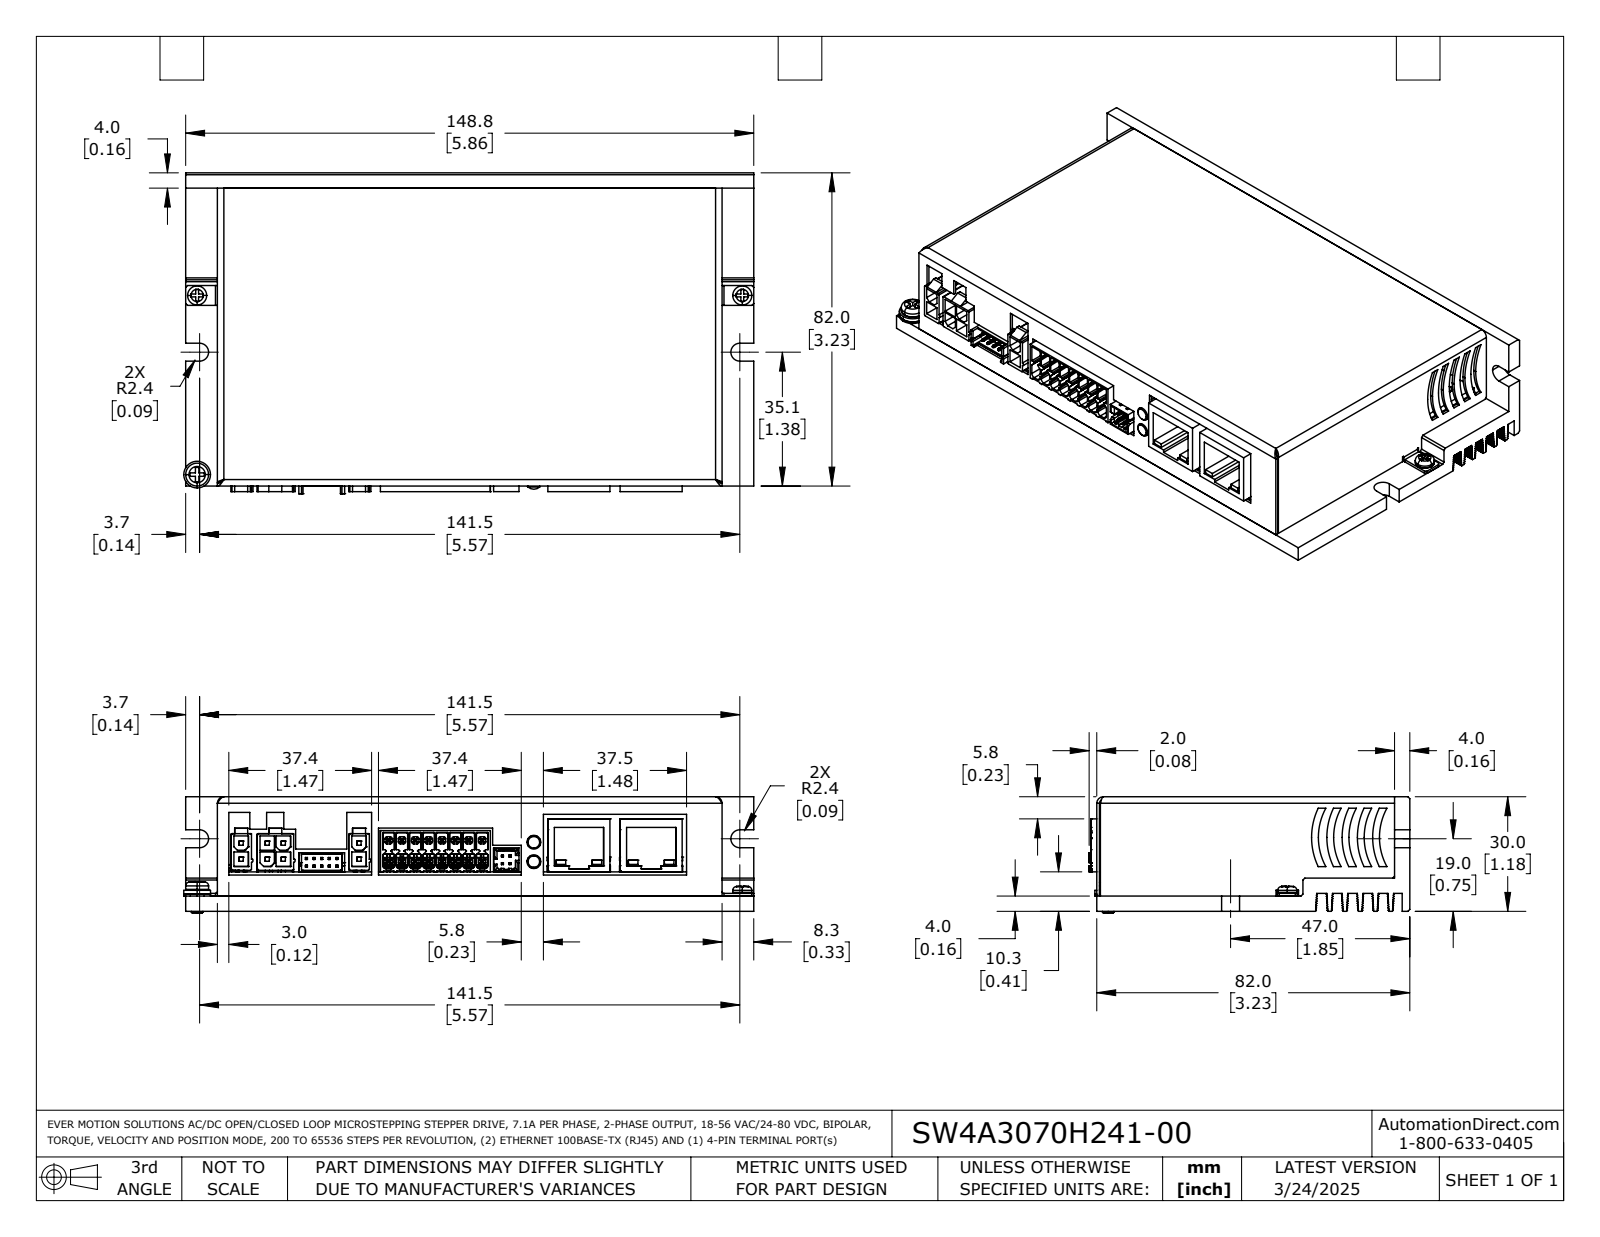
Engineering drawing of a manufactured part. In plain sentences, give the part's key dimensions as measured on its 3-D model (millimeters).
The part is named "SW4A3070H241-00C0680". Its 3-D file was written by "SolidWorks 2024 (AUTOMOTIVE_DESIGN)". It is 21 solids with 3854 faces: 2524 planar, 1109 cylindrical and 221 other. Overall it measures 149.3 by 84 by 30.5 millimeters. Its volume is 105 900 cubic millimeters and its surface area 111 800 square millimeters. Round holes: 30 of diameter 1, 18 of diameter 1.4, 16 of diameter 0.9, 14 of diameter 0.9, 9 of diameter 0.8, 8 of diameter 1.8, 7 of diameter 3.2, 6 of diameter 1.3, 6 of diameter 2.5, 6 of diameter 2.7, 4 of diameter 1.6, 4 of diameter 1.8. Round bosses or shafts: 3 of diameter 5, 3 of diameter 2.5, 2 of diameter 3, 1 of diameter 7, 1 of diameter 6, 1 of diameter 3, 1 of diameter 1.4, 1 of diameter 0.5. Partial cylindrical surfaces (rounded edges, fillets, slot ends): 144 of radius 0.1, 88 of radius 0.2, 19 of radius 0.3, 18 of radius 0.2, 18 of radius 0.9, 12 of radius 0.2, 10 of radius 0.2, 6 of radius 0.4. The main face-to-face distances are 0.7, 4, 25.3, 21.3, 20.6, 1.6, 19, 19.7, 8.7, 10.3. The hole center spacings are 2.5, 5.1, 3.6, 5.7, 16.3, 7.6, 5.6, 19.2.
